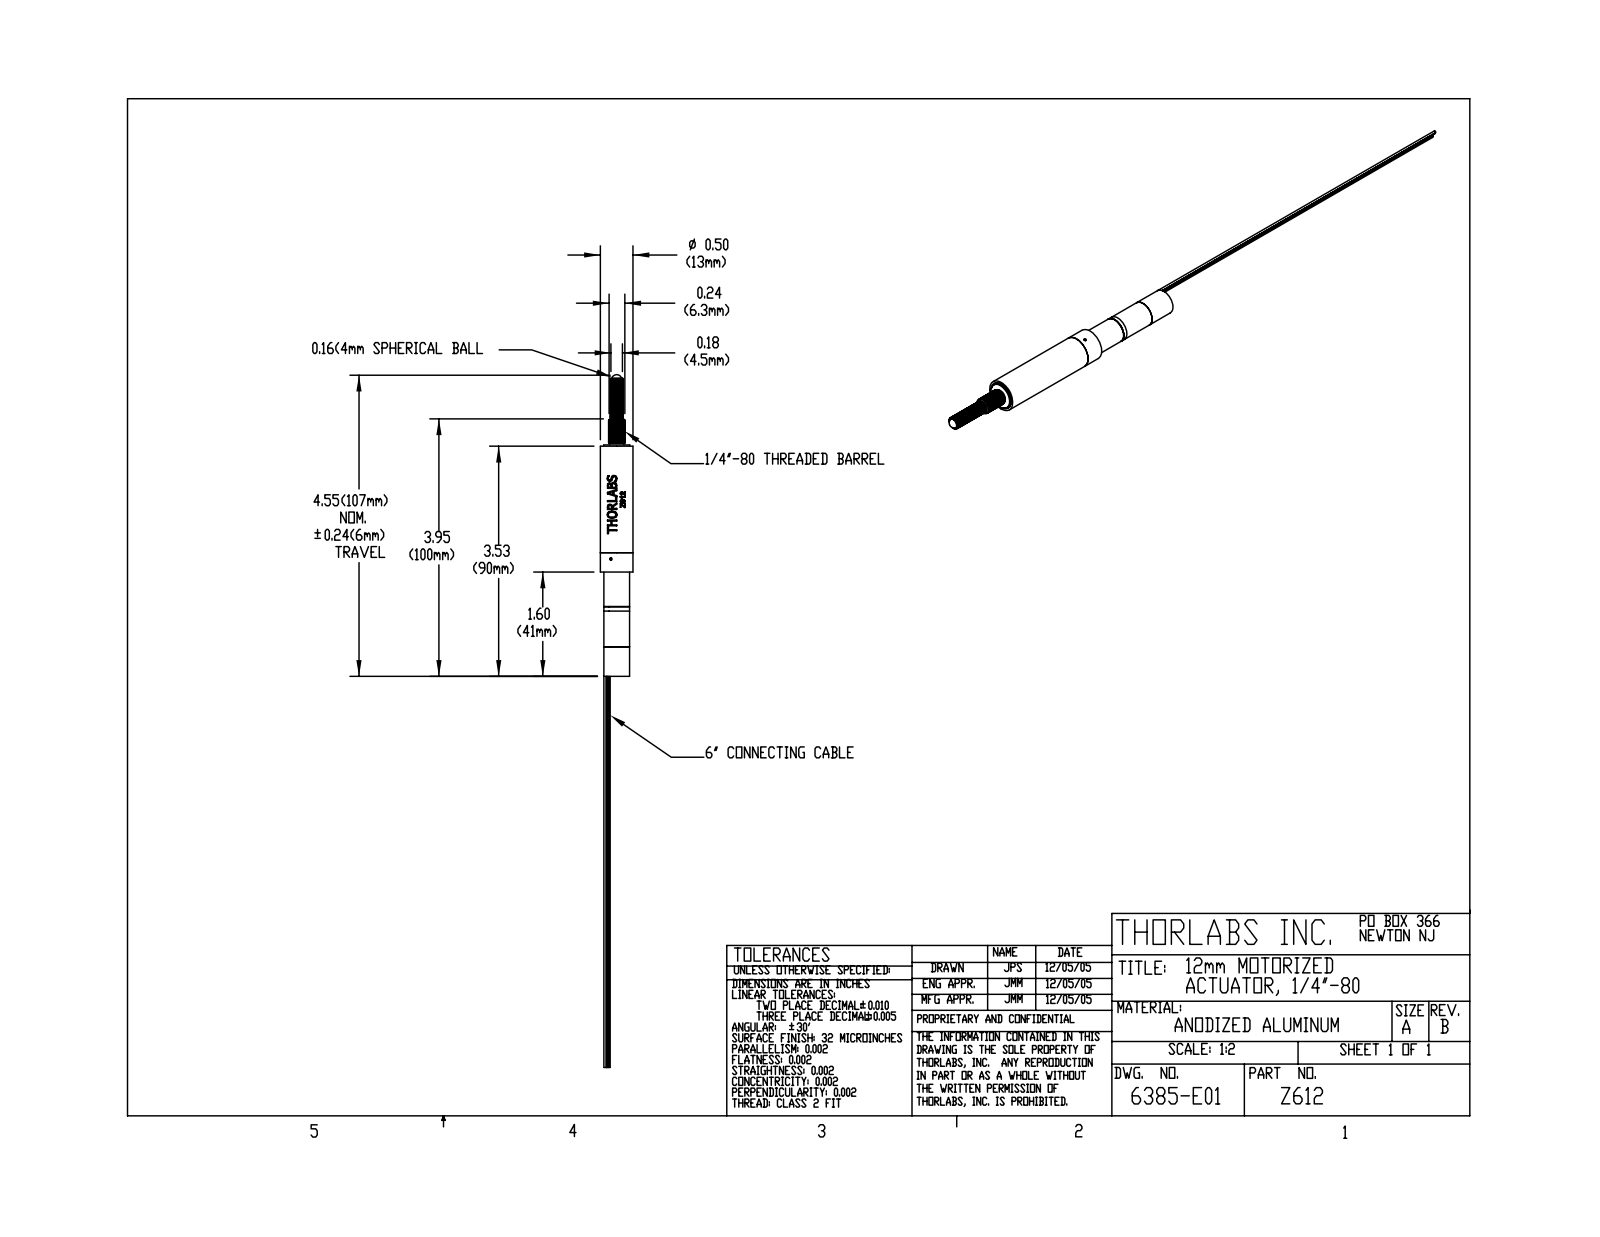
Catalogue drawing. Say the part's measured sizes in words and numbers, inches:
The part is named "6385-E0W". Its 3-D file was written by "SolidWorks 2007 (AUTOMOTIVE_DESIGN)". It is 0 solids with 266 faces: 22 planar, 227 cylindrical and 17 other. Overall it measures 10.627 by 0.5 by 0.5 inches. Round holes: 1 of diameter 0.038, 1 of diameter 0.156, 1 of diameter 0.375, 1 of diameter 0.433, 1 of diameter 0.46, 1 of diameter 0.48. Round bosses or shafts: 1 of diameter 0.5, 1 of diameter 0.403, 1 of diameter 0.394, 1 of diameter 0.394, 1 of diameter 0.25, 1 of diameter 0.22, 1 of diameter 0.197. Partial cylindrical surfaces (rounded edges, fillets, slot ends): 6 of radius 0.017. The main face-to-face distances are 0.453, 3.097, 3.55, 2.479, 0.618, 1.071, 1.89, 0.589, 1.207, 1.66.
